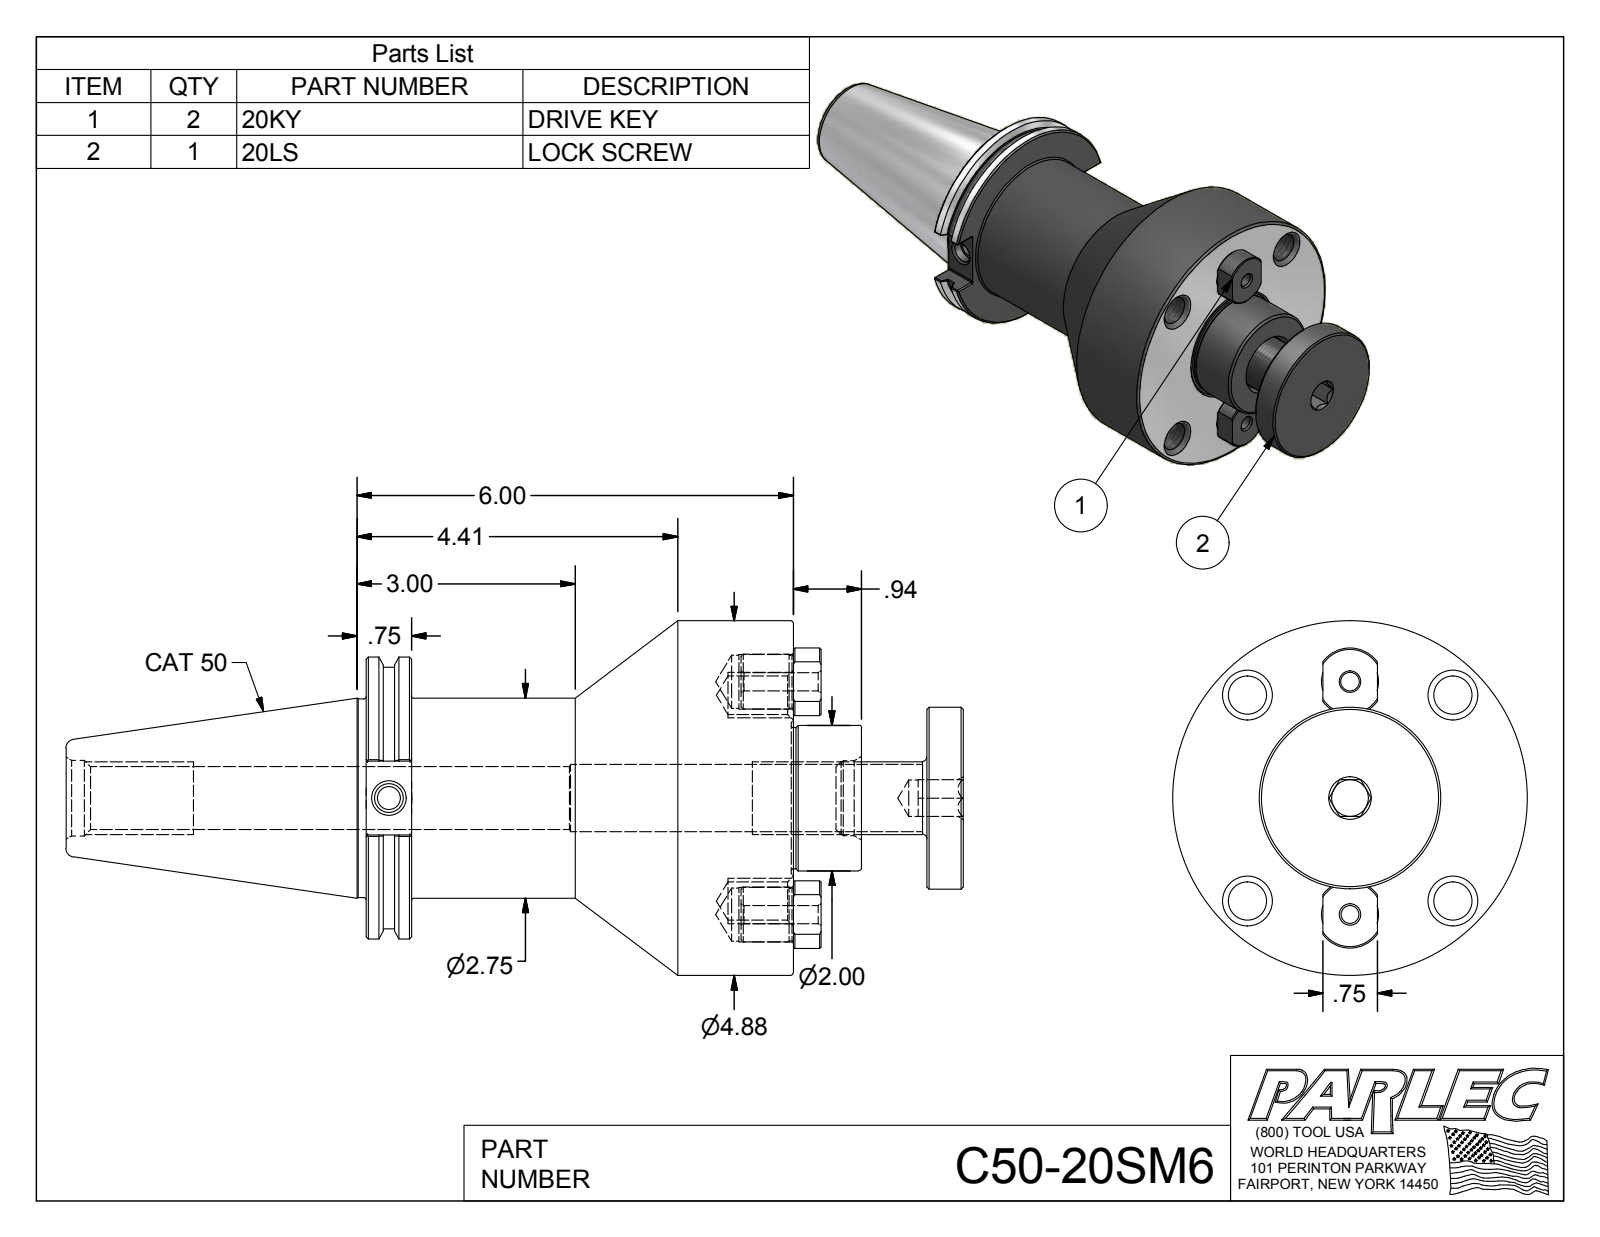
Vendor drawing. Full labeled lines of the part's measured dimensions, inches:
Part name (STEP PRODUCT): C50-20SM6; C50-20SM6-1; 20KY; 20LS
STEP written by: Autodesk Inventor 2012 (AUTOMOTIVE_DESIGN)
Units: inches
Bodies: 4 solids, 173 faces (57 planar, 50 cylindrical, 66 other)
Overall size (bounding box): 12.335 × 4.875 × 4.875
Volume: 80.4 in³ · Surface area: 206.8 in²
Round holes (diameter × count): ⌀0.527 ×4, ⌀0.25 ×2, ⌀0.73 ×2, ⌀0.75 ×2, ⌀0.315 ×1, ⌀0.399 ×1, ⌀0.502 ×1, ⌀0.865 ×1, ⌀0.923 ×1, ⌀1.03 ×1, ⌀1.038 ×1
Round bosses / shafts (diameter × count): ⌀0.755 ×2, ⌀0.72 ×2, ⌀4.875 ×1, ⌀3.875 ×1, ⌀3.594 ×1, ⌀2.75 ×1, ⌀2.73 ×1, ⌀2.5 ×1
Partial cylindrical surfaces — rounded edges, fillets, slot ends (radius × count): R0.02 ×12, R0.464 ×2
Main face-to-face distances: 2.335, 5.875, 8.21, 0.625, 5.25, 7.585, 7.71, 7.085, 1.835, 0.5
Hole centre spacings: 1.426, 2, 2.828, 3.33, 1.6, 4, 3.2
